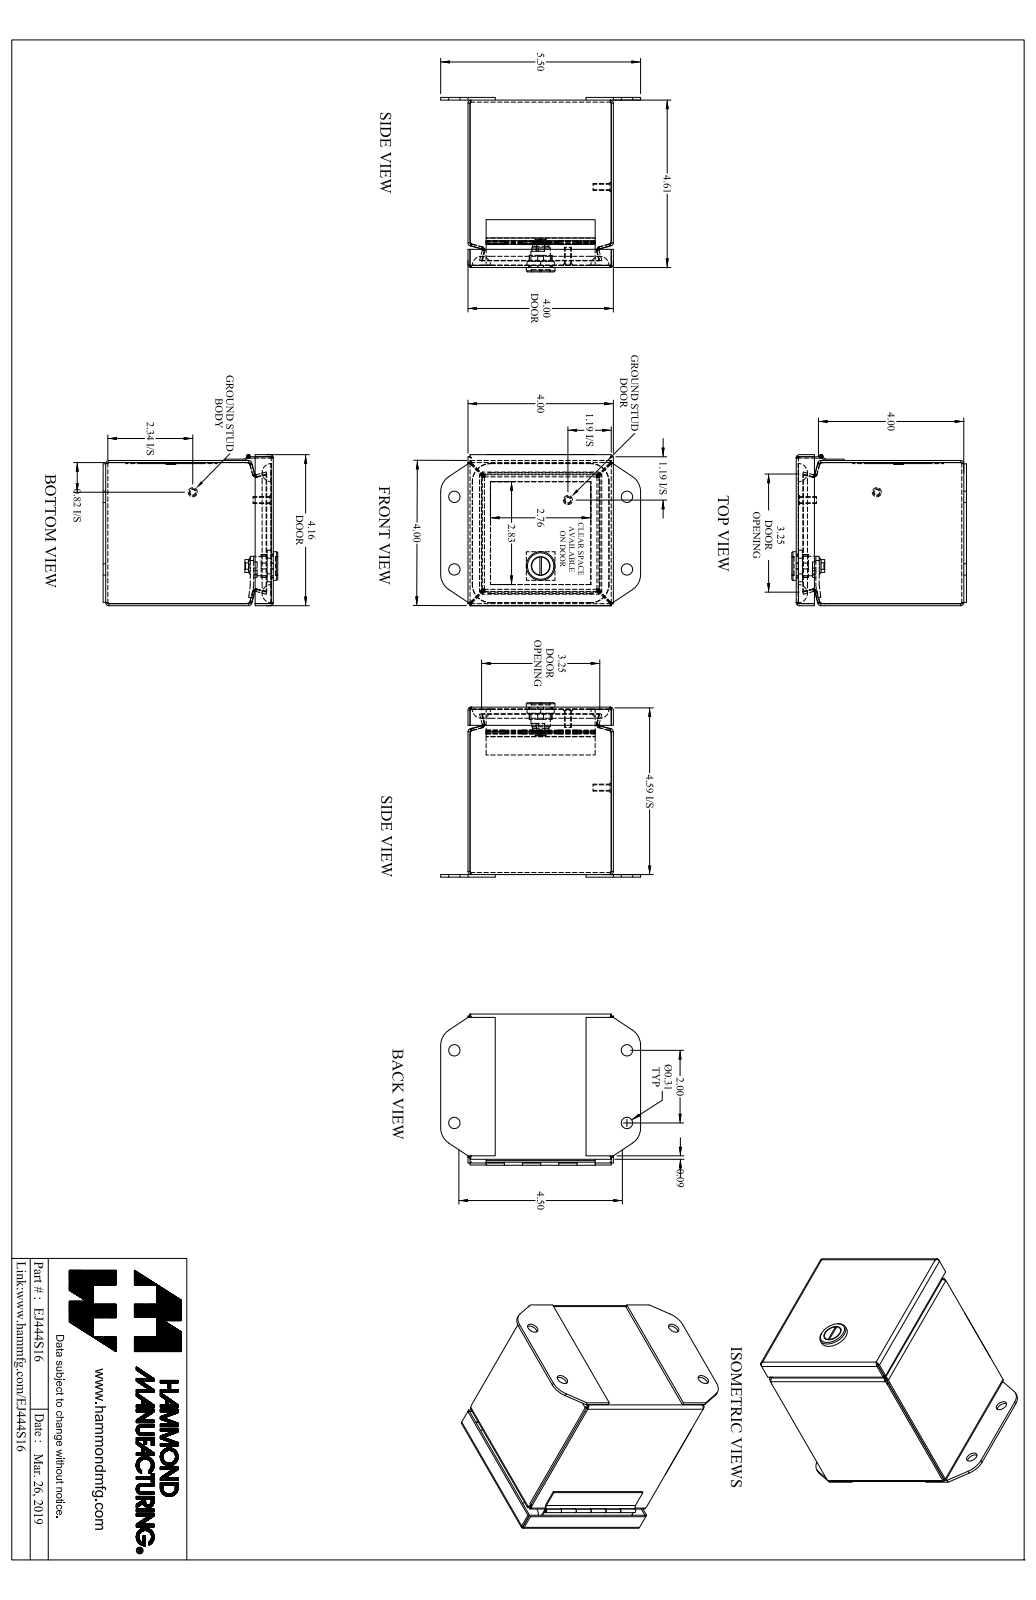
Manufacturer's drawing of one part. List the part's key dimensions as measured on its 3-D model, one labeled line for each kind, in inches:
Part name (STEP PRODUCT): EJ444S16_Default
STEP written by: SolidWorks 2019 (CONFIG_CONTROL_DESIGN)
Units: inches
Bodies: 11 solids, 438 faces (248 planar, 134 cylindrical, 56 other)
Overall size (bounding box): 5.5 × 4.805 × 4.165
Volume: 8.667 in³ · Surface area: 288.6 in²
Round holes (diameter × count): ⌀0.313 ×4, ⌀0.05 ×1, ⌀0.516 ×1
Round bosses / shafts (diameter × count): ⌀0.25 ×2, ⌀0.19 ×2, ⌀0.788 ×1, ⌀0.535 ×1, ⌀0.496 ×1, ⌀0.435 ×1, ⌀0.1 ×1, ⌀0.045 ×1
Partial cylindrical surfaces — rounded edges, fillets, slot ends (radius × count): R0.029 ×16, R0.086 ×16, R0.281 ×12, R0.25 ×4, R0.499 ×4, R0.5 ×4, R0.06 ×2, R0.03 ×1
Main face-to-face distances: 0.057, 3.943, 4.554, 3.886, 4, 4.611, 4.497, 4.683, 4.626, 0.129
Hole centre spacings: 2, 2.377, 3.046, 4.75, 5.154
